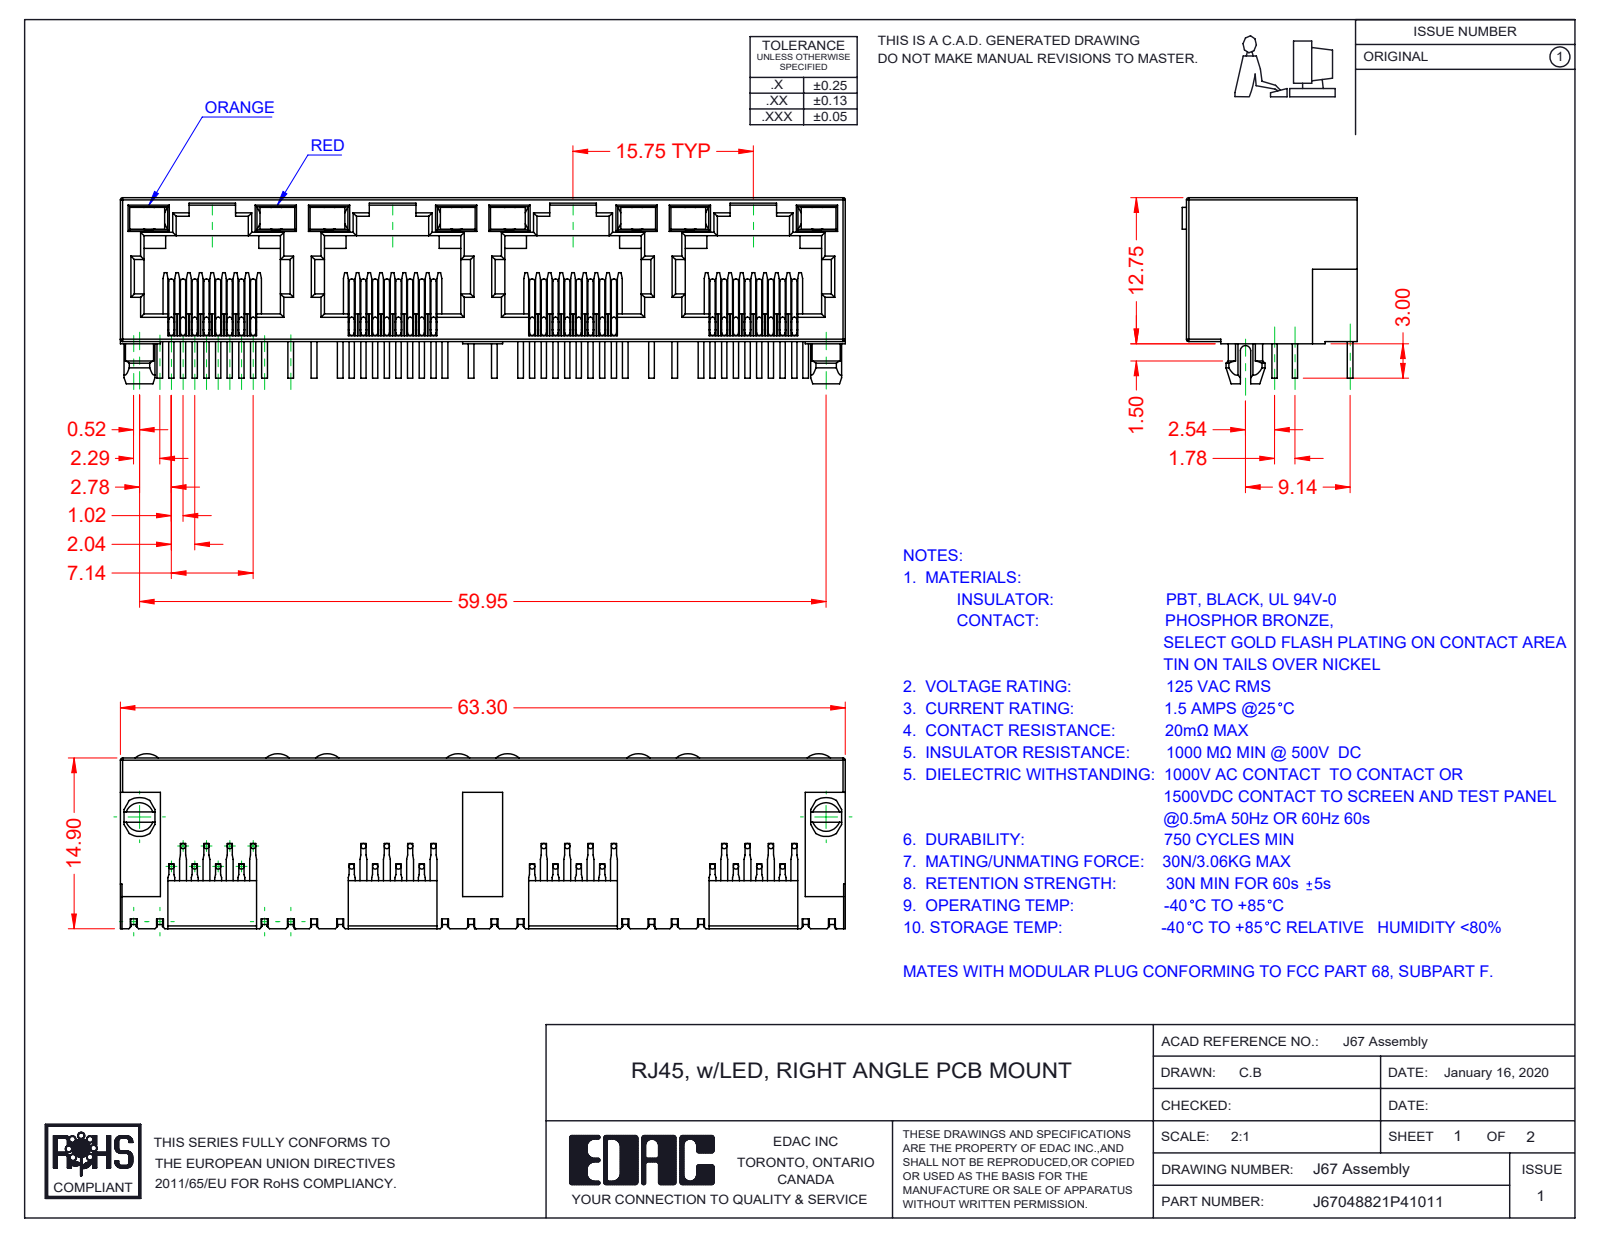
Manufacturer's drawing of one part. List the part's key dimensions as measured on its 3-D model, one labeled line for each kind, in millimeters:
Part name (STEP PRODUCT): 67 Contacts; 67 LED LH_4-Orange; 67 Insulator; 67 LED RH_2-Red (+1 more)
STEP written by: SolidWorks 2016 (CONFIG_CONTROL_DESIGN)
Units: millimetres
Bodies: 41 solids, 2465 faces (1781 planar, 476 cylindrical, 208 other)
Overall size (bounding box): 63.3 × 16.25 × 15.28
Volume: 5 159 mm³ · Surface area: 11 573 mm²
Round bosses / shafts (diameter × count): ⌀0.46 ×96
Partial cylindrical surfaces — rounded edges, fillets, slot ends (radius × count): R0.2 ×66, R0.3 ×29, R0.45 ×9, R1.55 ×8, R1.5 ×2, R1.7 ×2, R0.35 ×1, R1 ×1
Main face-to-face distances: 0.5, 12.55, 1.89, 0.89, 10, 15.75, 1, 1.39, 11, 11.89
